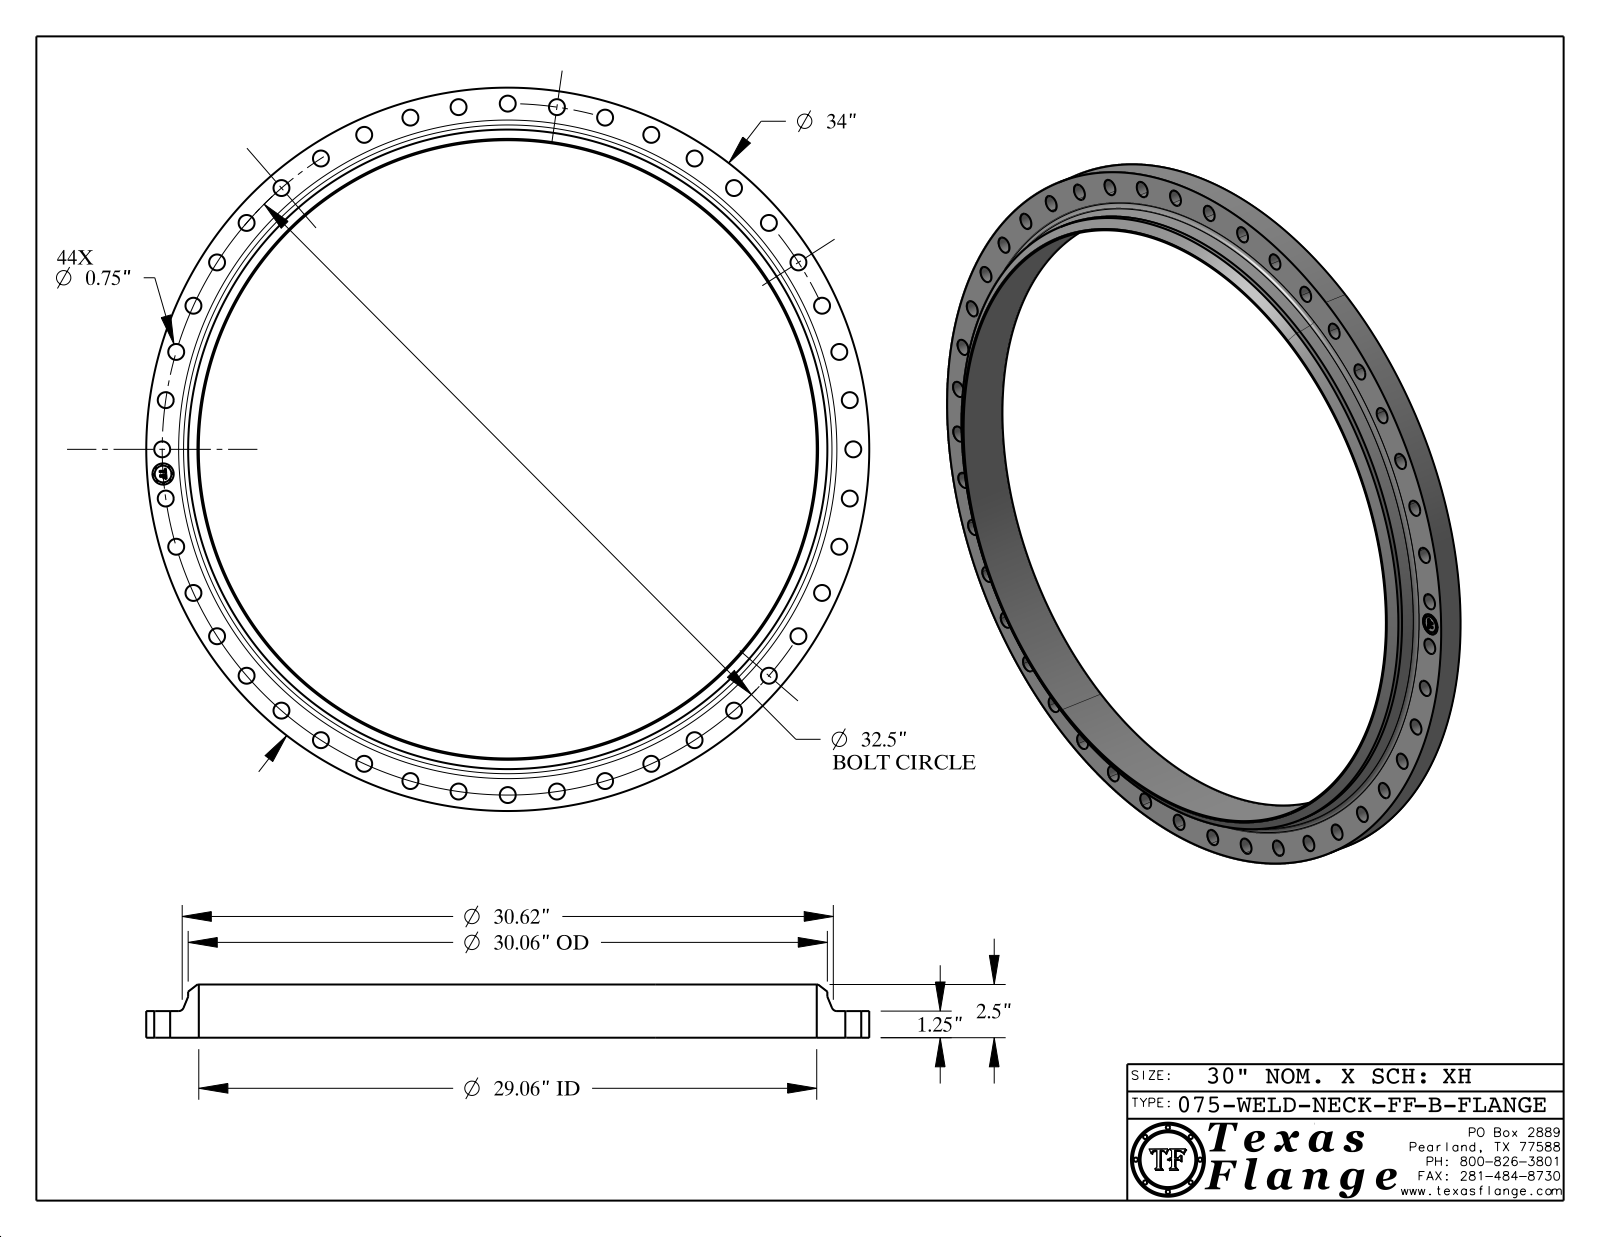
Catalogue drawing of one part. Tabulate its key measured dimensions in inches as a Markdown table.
| quantity | value |
| --- | --- |
| part name | 075-WELD-NECK-FF, Series B |
| STEP written by | CATIA V5 STEP AP214 (AUTOMOTIVE_DESIGN) |
| units | inches |
| bodies | 1 solid, 488 faces (368 planar, 114 cylindrical, 6 other) |
| overall size | 34 × 34 × 2.5 |
| volume | 342.2 in³ |
| surface area | 1 014 in² |
| round holes (diameter × count) | 0.75 × 44, 1 × 1, 29.06 × 1 |
| round bosses / shafts (diameter × count) | 0.061 × 8, 34 × 1, 30.06 × 1, 0.788 × 1 |
| main face-to-face distances | 1.25, 2.5, 1.235, 0.015, 1.265, 0.298, 0.292, 0.054, 0.193, 0.248 |
| hole center spacings | 16.25, 32.417, 32.169, 31.183, 9.156, 4.625, 29.563, 31.757 |
